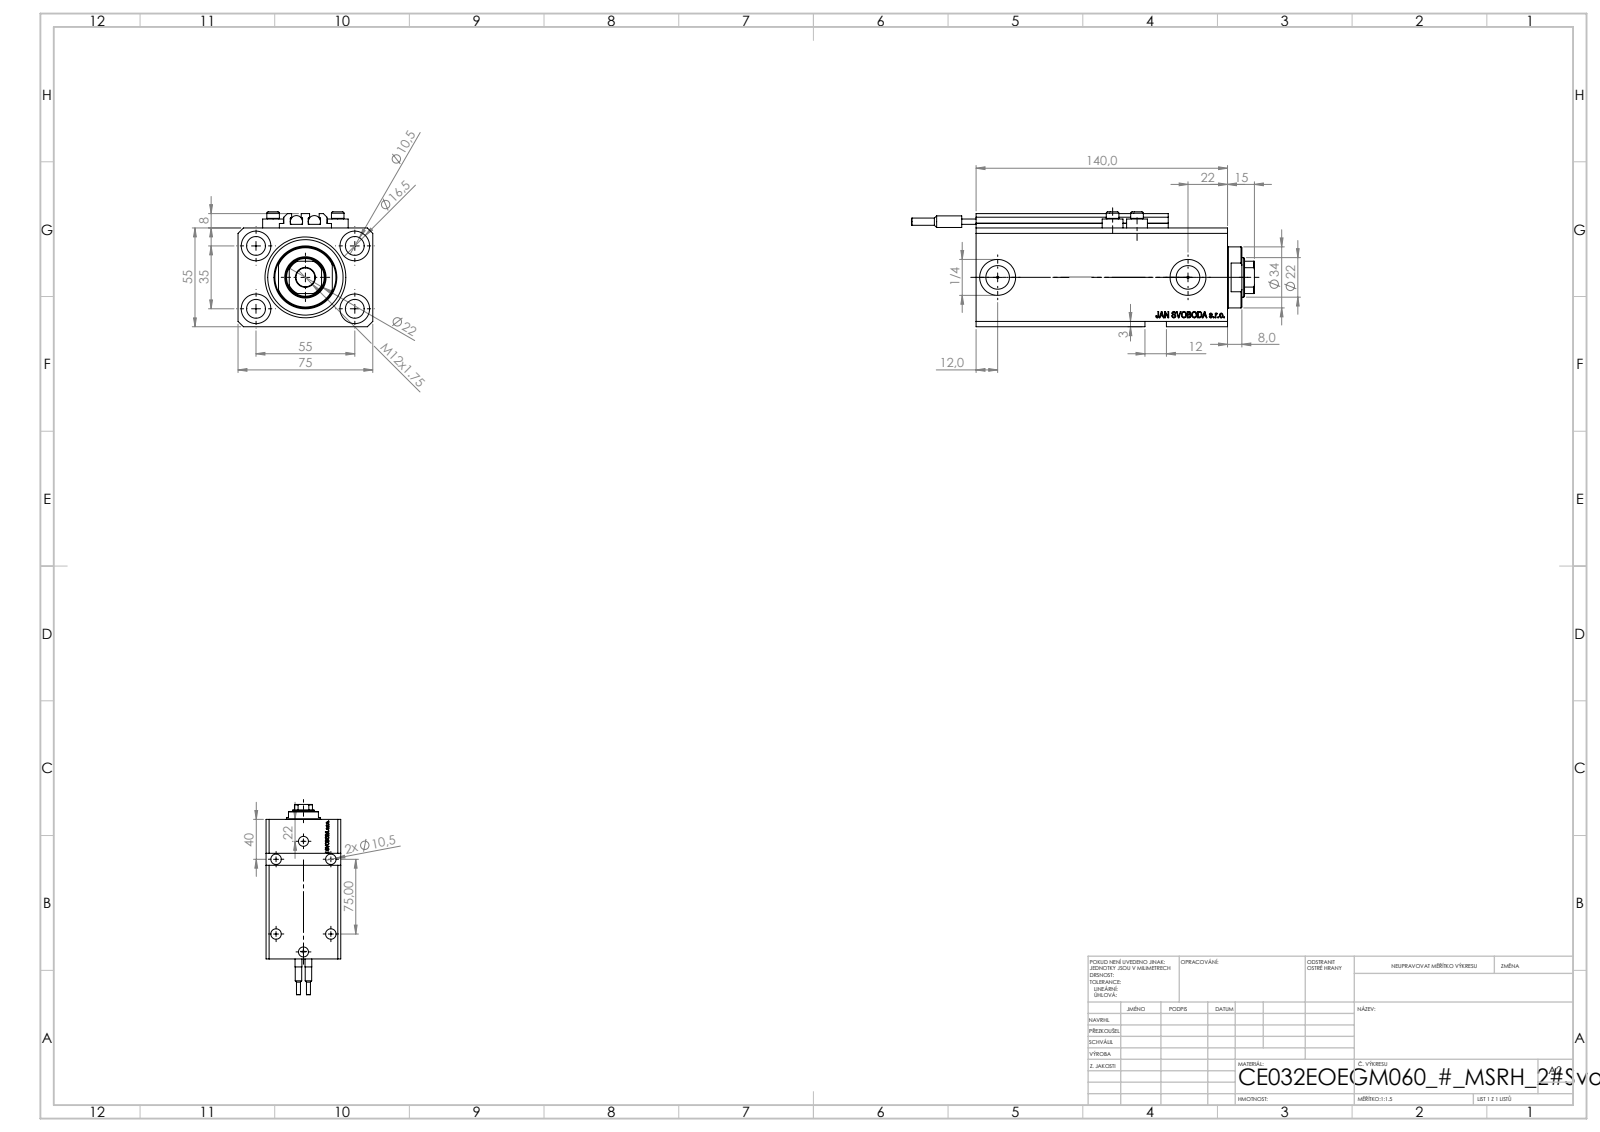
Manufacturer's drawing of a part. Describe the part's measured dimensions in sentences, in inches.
The part is named "V250CE_VC_E; ALLEN BOLT V250CE; SWITCH_V250CE; V250CE_C_VCP (+1 more)". Its 3-D file was written by "SolidWorks 2019 (CONFIG_CONTROL_DESIGN)". It is 10 solids with 1136 faces: 546 planar, 158 cylindrical and 432 other. Overall it measures 7.52 by 2.953 by 2.52 inches. Its volume is 29.83 cubic inches and its surface area 183 square inches. Round holes: 9 of diameter 0.413, 4 of diameter 0.049, 4 of diameter 0.157, 4 of diameter 0.65, 2 of diameter 0.394, 2 of diameter 0.518, 2 of diameter 0.787, 1 of diameter 0.866, 1 of diameter 1.26, 1 of diameter 1.772. Round bosses or shafts: 4 of diameter 0.457, 4 of diameter 0.276, 2 of diameter 0.268, 2 of diameter 0.256, 2 of diameter 0.157, 1 of diameter 1.339. Partial cylindrical surfaces (rounded edges, fillets, slot ends): 10 of radius 0.008, 1 of radius 0.413. The main face-to-face distances are 2.165, 2.953, 0.118, 2.244, 0.591, 5.512, 4.921, 0.39, 0.079, 0.098. The hole center spacings are 1.283, 1.294, 2.165, 3.818, 0.535, 0.555, 1.016, 1.283.
